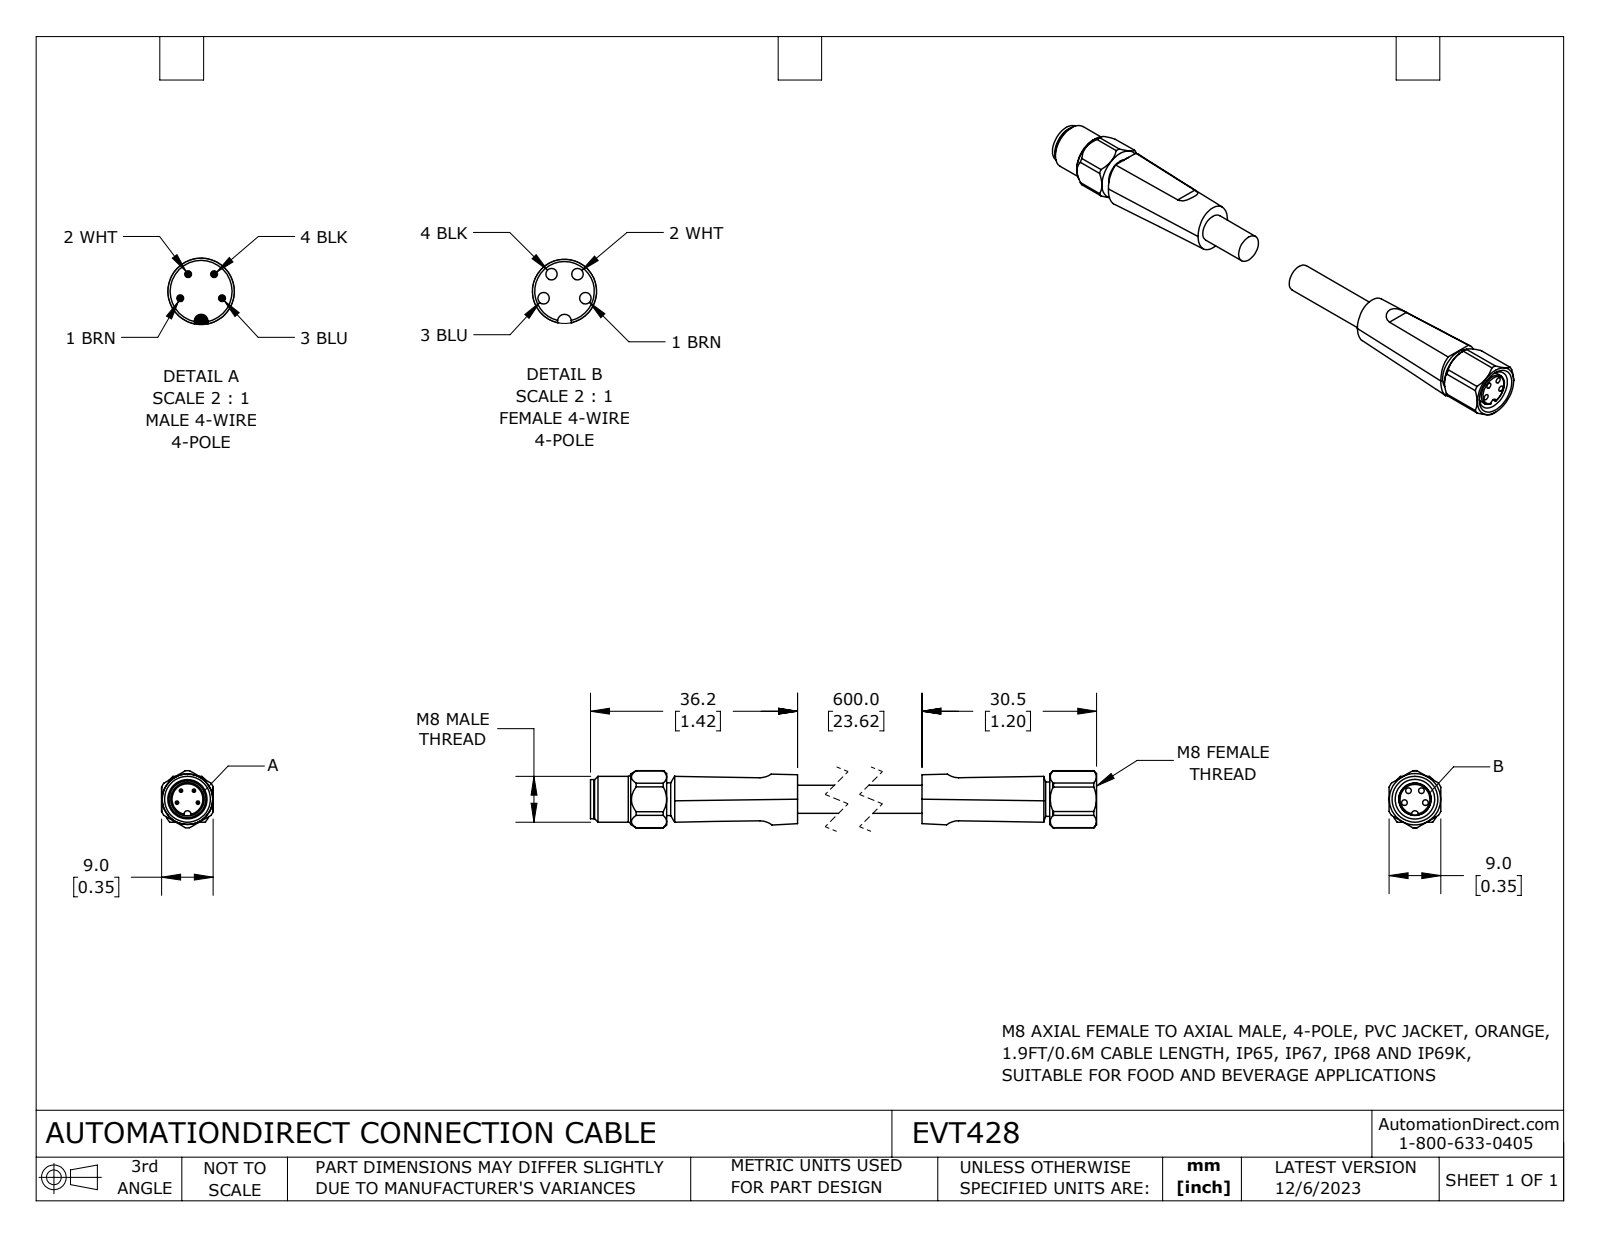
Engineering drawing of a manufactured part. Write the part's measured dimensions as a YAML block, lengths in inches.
part_name: "EVT428_FEMALE; EVT428; EVT428_MALE"
step_written_by: "SolidWorks 2023 (CONFIG_CONTROL_DESIGN)"
units: inches
bodies: {solids: 2, faces: 150, planar: 47, cylindrical: 58, other: 45}
overall_size: [4.173, 0.393, 0.354]
volume: 0.244
surface_area: 4.751
round_holes:
  - {diameter: 0.039, count: 4}
  - {diameter: 0.228, count: 1}
  - {diameter: 0.272, count: 1}
round_bosses_or_shafts:
  - {diameter: 0.023, count: 4}
  - {diameter: 0.315, count: 1}
  - {diameter: 0.27, count: 1}
  - {diameter: 0.248, count: 1}
  - {diameter: 0.236, count: 1}
  - {diameter: 0.224, count: 1}
  - {diameter: 0.222, count: 1}
  - {diameter: 0.193, count: 1}
partial_cylinders:
  - {radius: 0.133, count: 4}
  - {radius: 0.024, count: 1}
  - {radius: 0.196, count: 1}
  - {radius: 0.196, count: 1}
face_to_face_distances: [0.354, 0.26, 0.26, 0.354, 3.327, 1.201, 2.449, 0.878, 0.9, 1.549]
hole_center_spacings: [0.074, 0.076, 0.087, 0.143, 0.089, 0.143]
